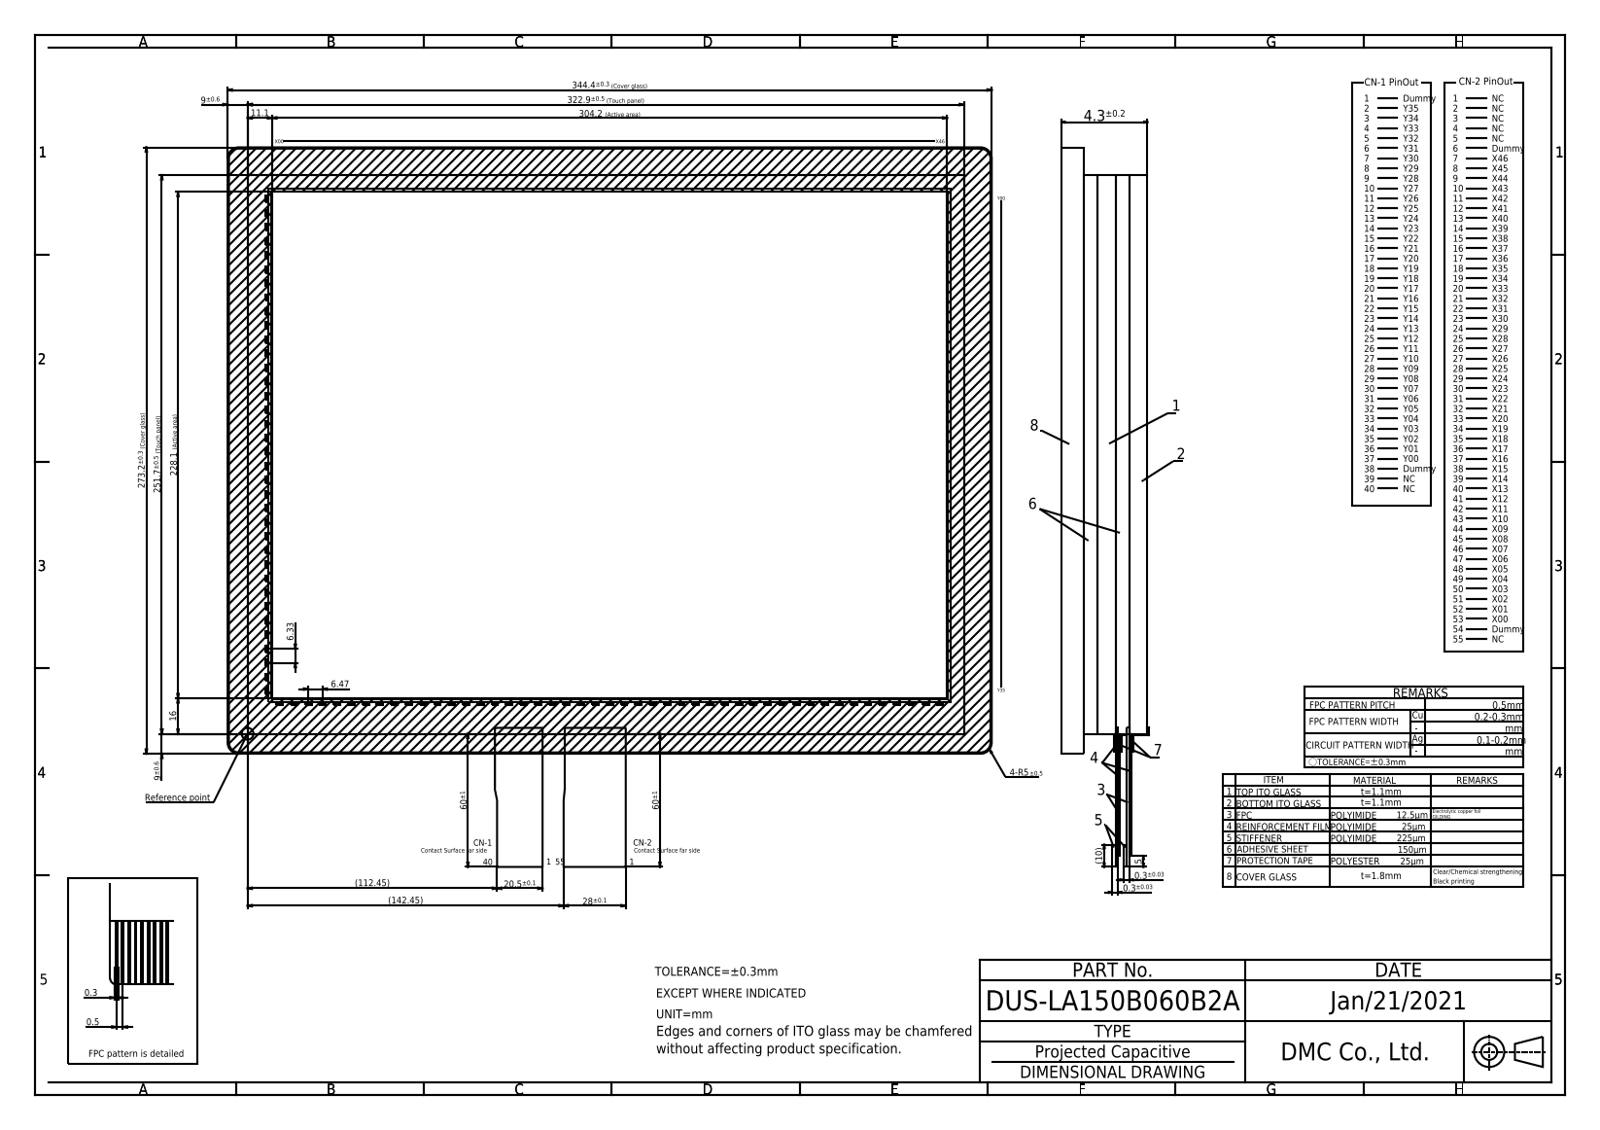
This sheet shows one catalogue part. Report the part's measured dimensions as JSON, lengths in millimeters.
{"part_name": "DUS-LA150B060B2A", "step_written_by": "Autodesk Inventor 2020 (CONFIG_CONTROL_DESIGN)", "units": "millimeters", "bodies": {"solids": 1, "faces": 425, "planar": 420, "cylindrical": 5, "other": 0}, "overall_size": [482.16, 382.48, 4.3], "volume_mm3": 365982, "surface_area_mm2": 338020, "partial_cylinders_radius": [[5, 4], [0.2, 1]], "face_to_face_distances": [1.8, 2.5, 4.3, 2.4, 1.9, 1.25, 1.15, 1.35, 3.15, 3.05]}
